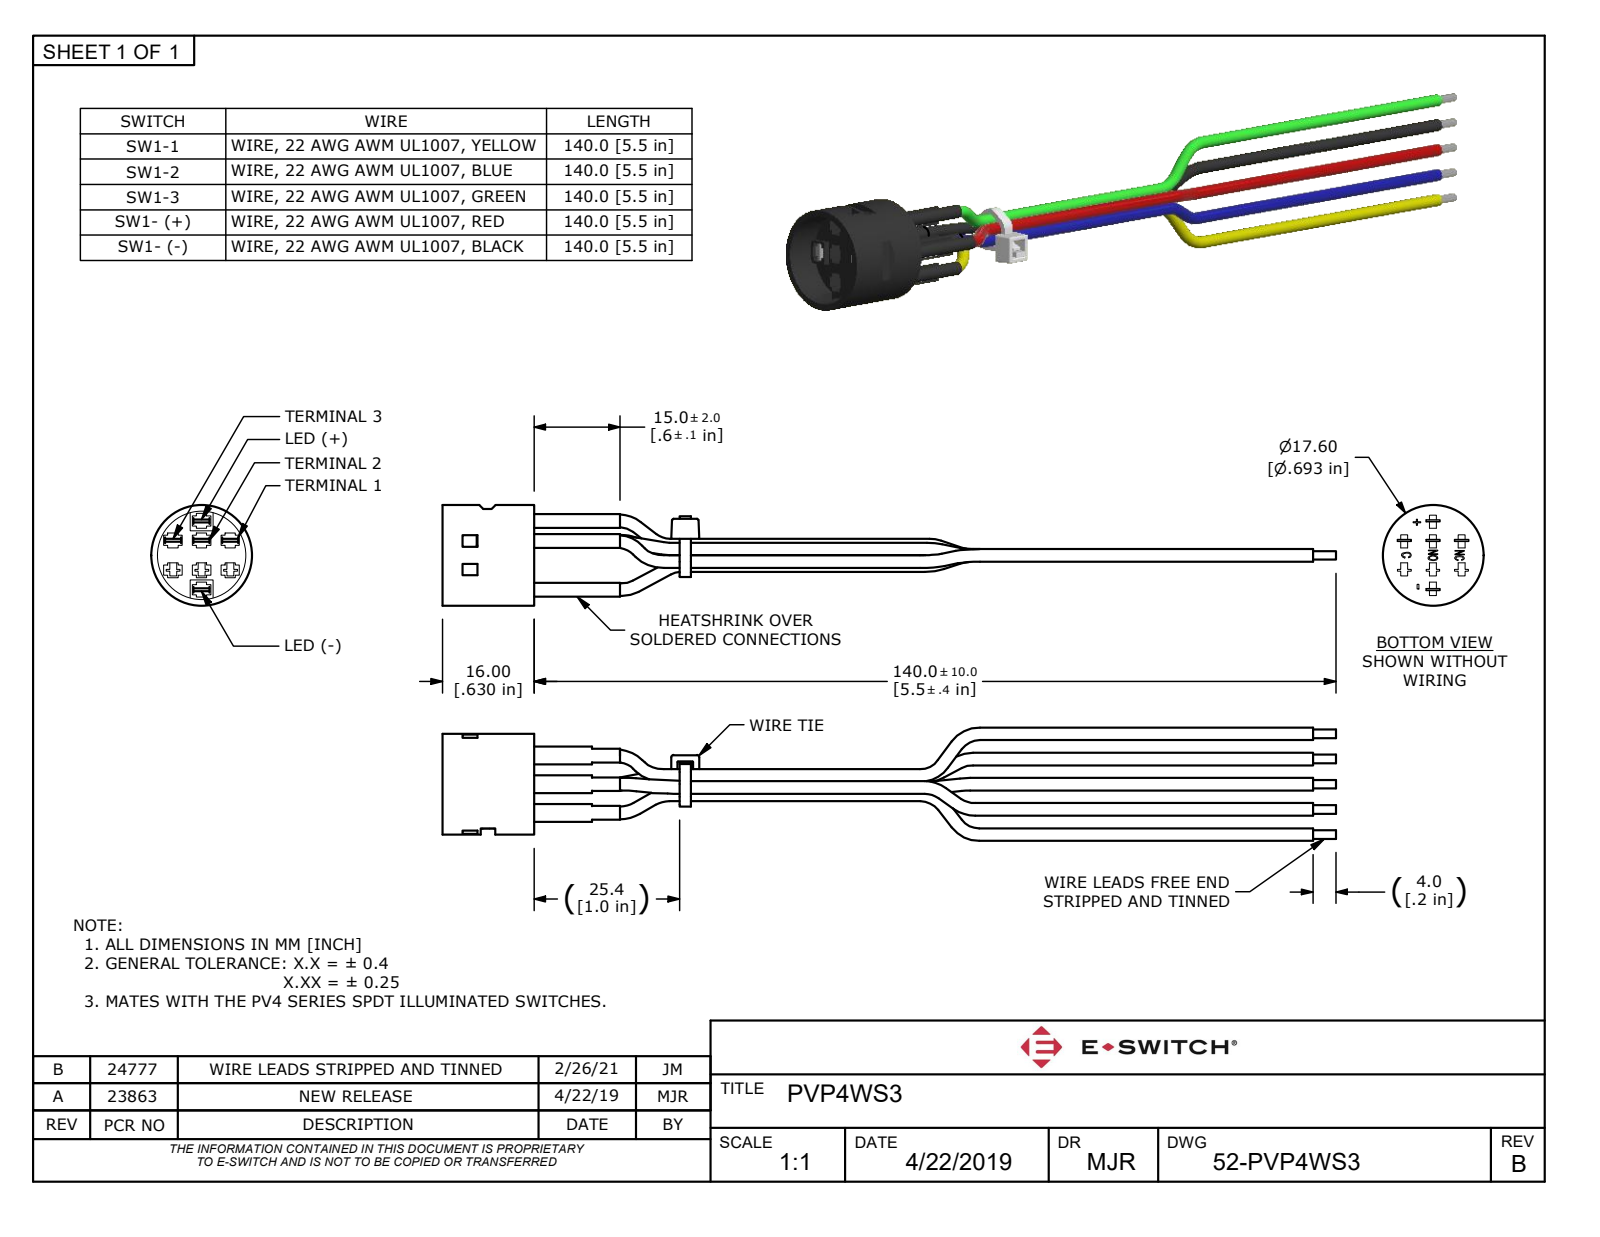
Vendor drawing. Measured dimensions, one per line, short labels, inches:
name: PVP4WS3
written by: Autodesk Inventor 2018 (AP242_MANAGED_MODEL_BASED_3D_ENGINEERING_MIM_LF)
unit: in
bodies: 1 solid, 662 faces (493 planar, 73 cylindrical, 96 other)
size: 6.142 × 0.78 × 0.693
volume: 0.321 in³; area: 12.03 in²
holes: 1× ⌀0.606
bosses: 21× ⌀0.087, 5× ⌀0.094, 5× ⌀0.059, 1× ⌀0.693
rounds: 14× R0.008, 14× R0.01, 4× R0.043, 4× R0.079
face distances: 0.02, 0.197, 0.39, 0.098, 0.026, 0.071, 0.016, 0.169, 0.24, 0.126
